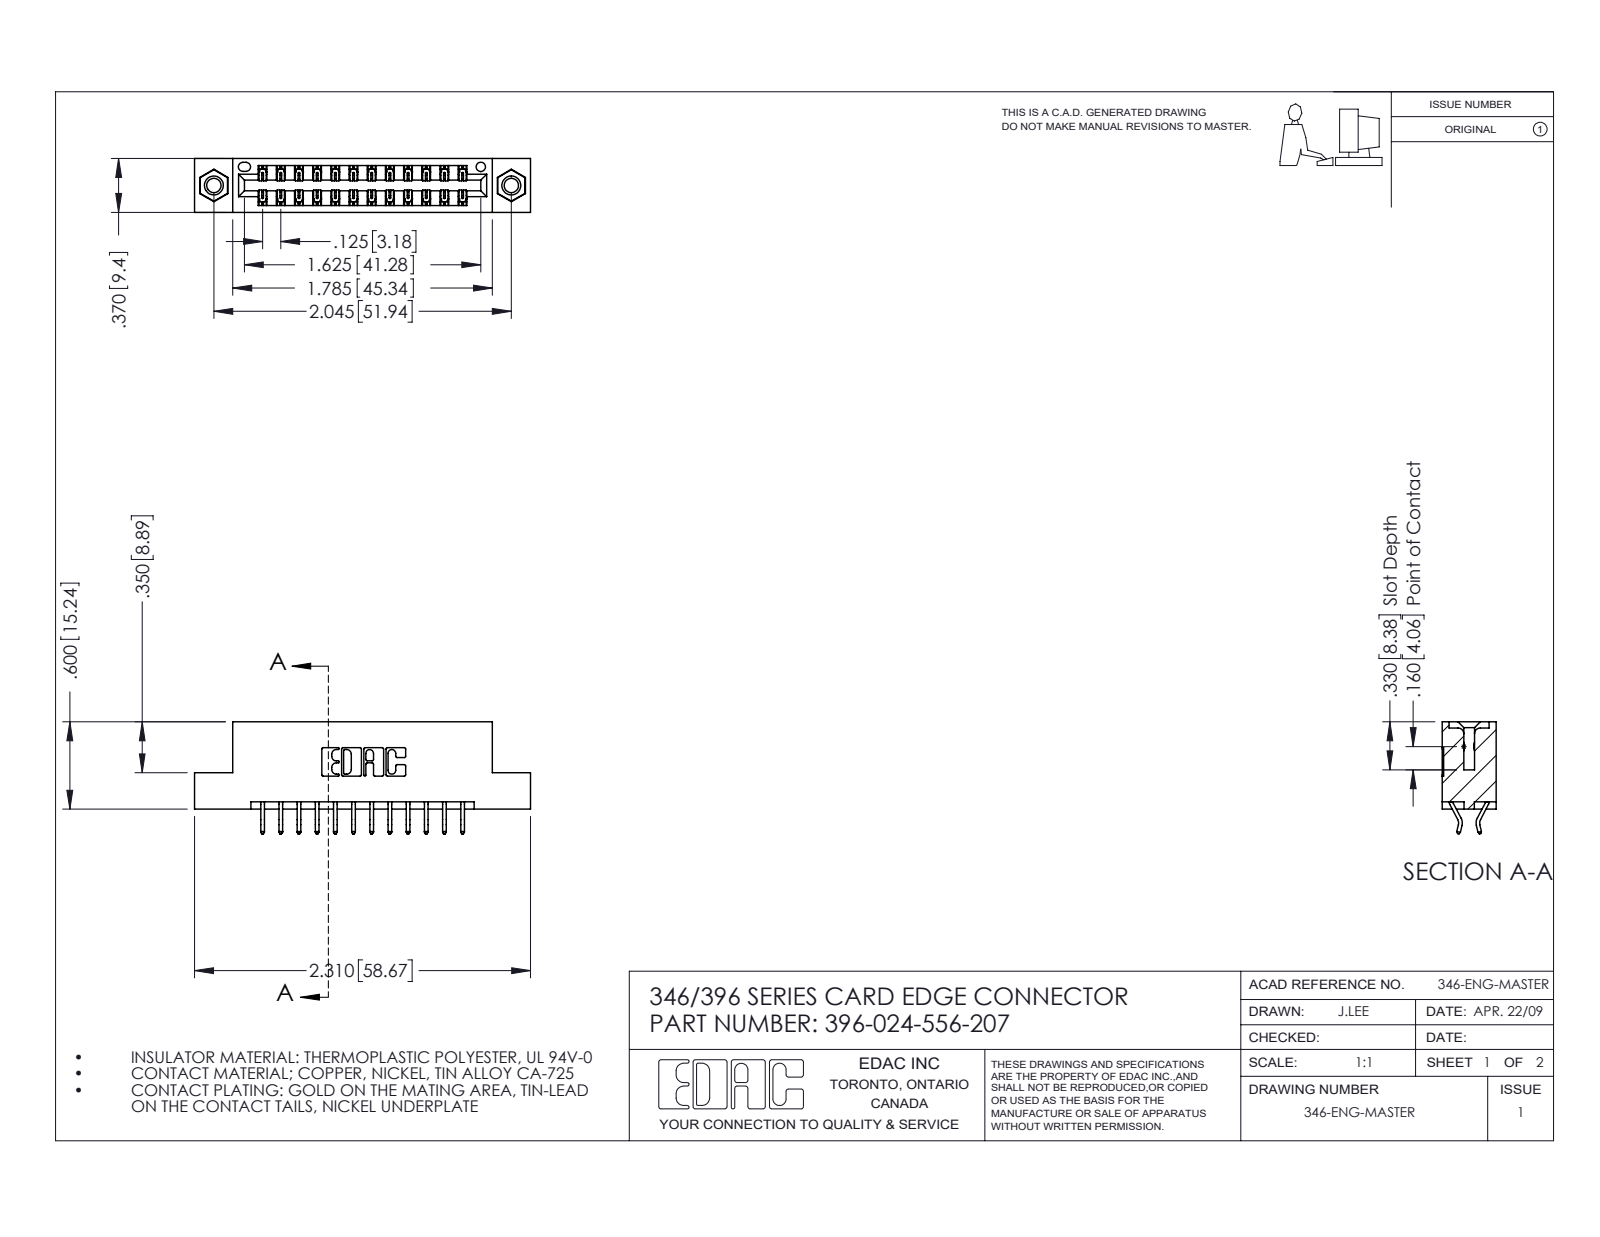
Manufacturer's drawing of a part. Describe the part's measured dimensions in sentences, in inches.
The part is named "396-024-556-207; 345-250-001_345-250-005-103; 345-292-001_556 Tail; 346 Part_Flush Mounting Lugs - 0.156 Dia-TI". Its 3-D file was written by "SolidWorks 2016 (CONFIG_CONTROL_DESIGN)". It is 27 solids with 1574 faces: 1044 planar, 514 cylindrical and 16 other. Overall it measures 2.31 by 0.77 by 0.37 inches. Its volume is 0.334 cubic inches and its surface area 10.95 square inches. Round holes: 2 of diameter 0.098, 2 of diameter 0.125, 2 of diameter 0.156, 1 of diameter 0.064. Round bosses or shafts: 2 of diameter 0.155. Partial cylindrical surfaces (rounded edges, fillets, slot ends): 36 of radius 0.006, 22 of radius 0.01, 6 of radius 0.007, 6 of radius 0.031, 3 of radius 0.026, 2 of radius 0.01, 2 of radius 0.014, 2 of radius 0.022. The main face-to-face distances are 0.25, 0.048, 0.322, 0.37, 0.025, 0.072, 0.298, 0.275, 0.148, 0.222. The hole center spacings are 0.246, 1.839, 2.045.
